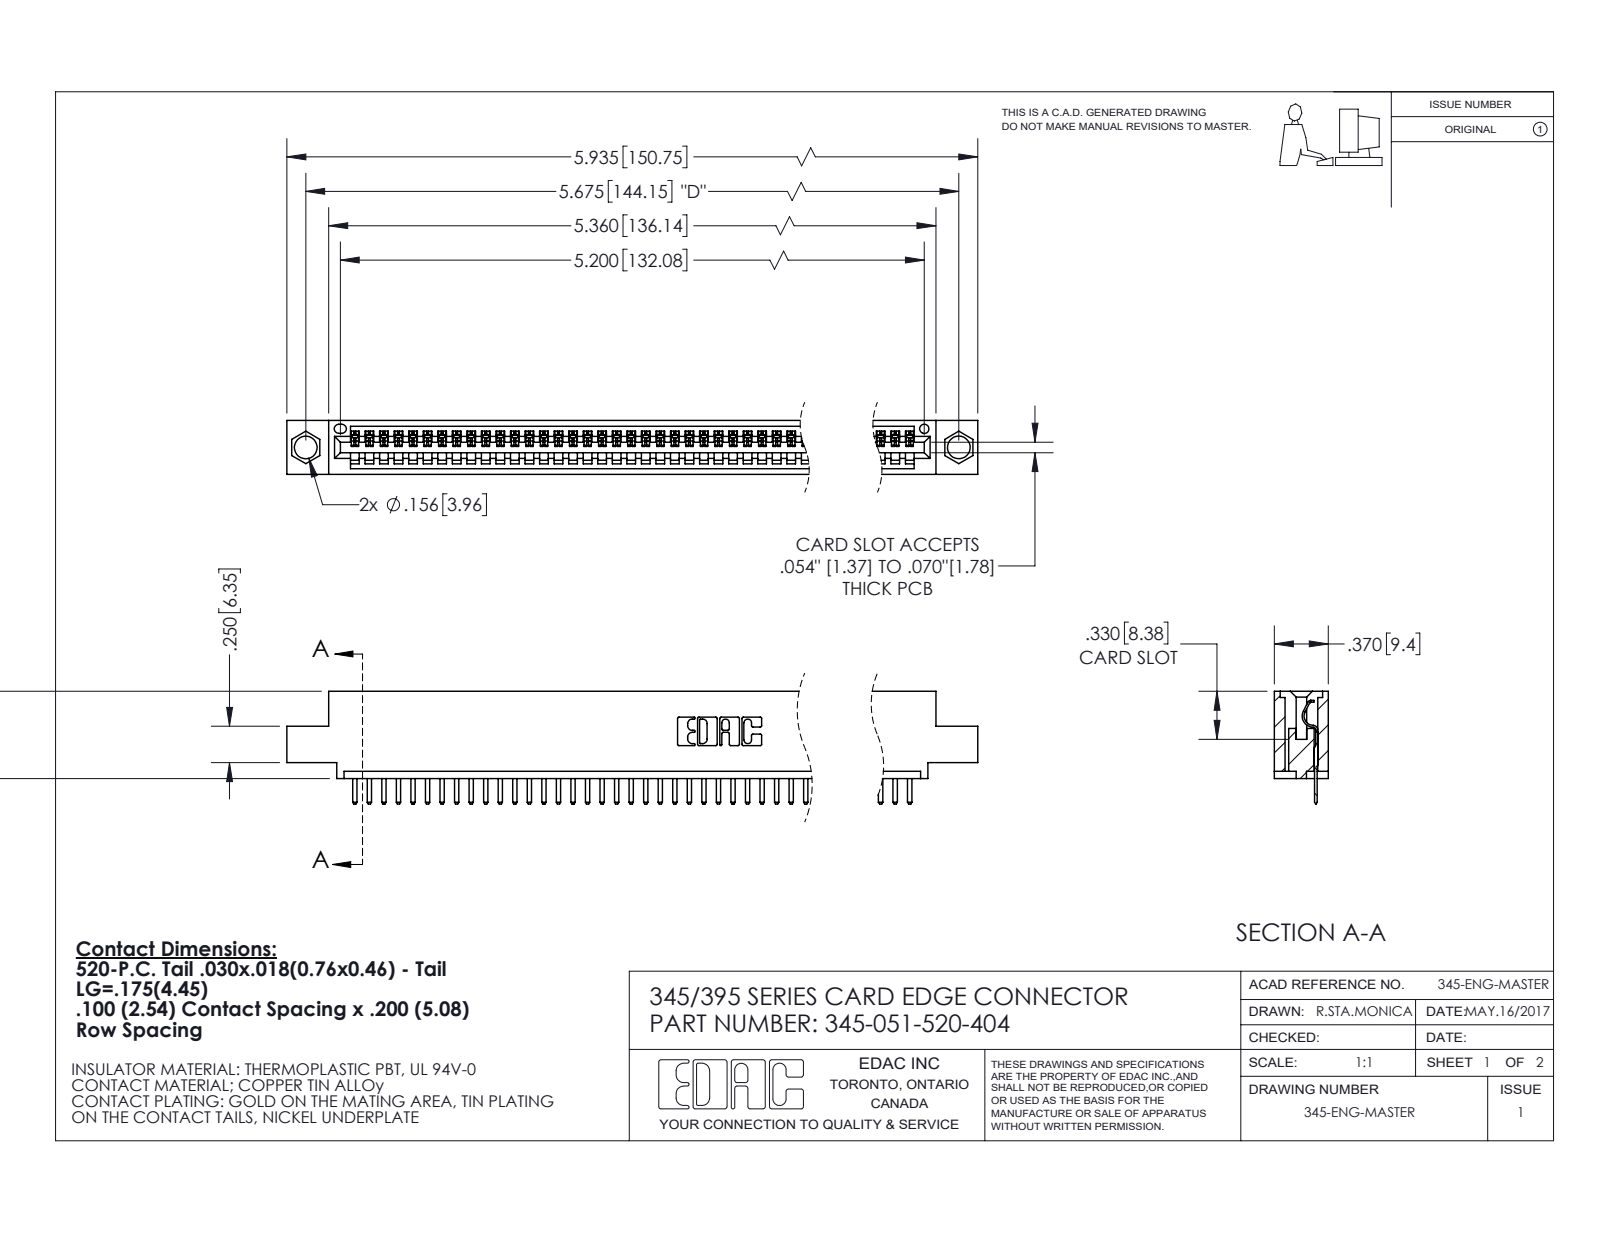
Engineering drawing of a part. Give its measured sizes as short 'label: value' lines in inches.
name: 345-292-001_345-293-120; 345-051-520-404; 345 Part_0.110 Offset - 0.156 Dia-TI
written by: SolidWorks 2020 (CONFIG_CONTROL_DESIGN)
unit: in
bodies: 52 solids, 3306 faces (2240 planar, 1066 cylindrical, 0 other)
size: 5.935 × 0.775 × 0.37
volume: 0.858 in³; area: 28.3 in²
holes: 2× ⌀0.156, 1× ⌀0.064
rounds: 104× R0.01, 102× R0.006, 22× R0.01, 6× R0.007, 6× R0.031, 3× R0.026, 2× R0.031, 2× R0.04
face distances: 0.298, 0.072, 0.37, 0.2, 0.098, 0.272, 0.025, 0.225, 0.072, 0.149
hole spacings: 0.27, 5.439, 5.675
